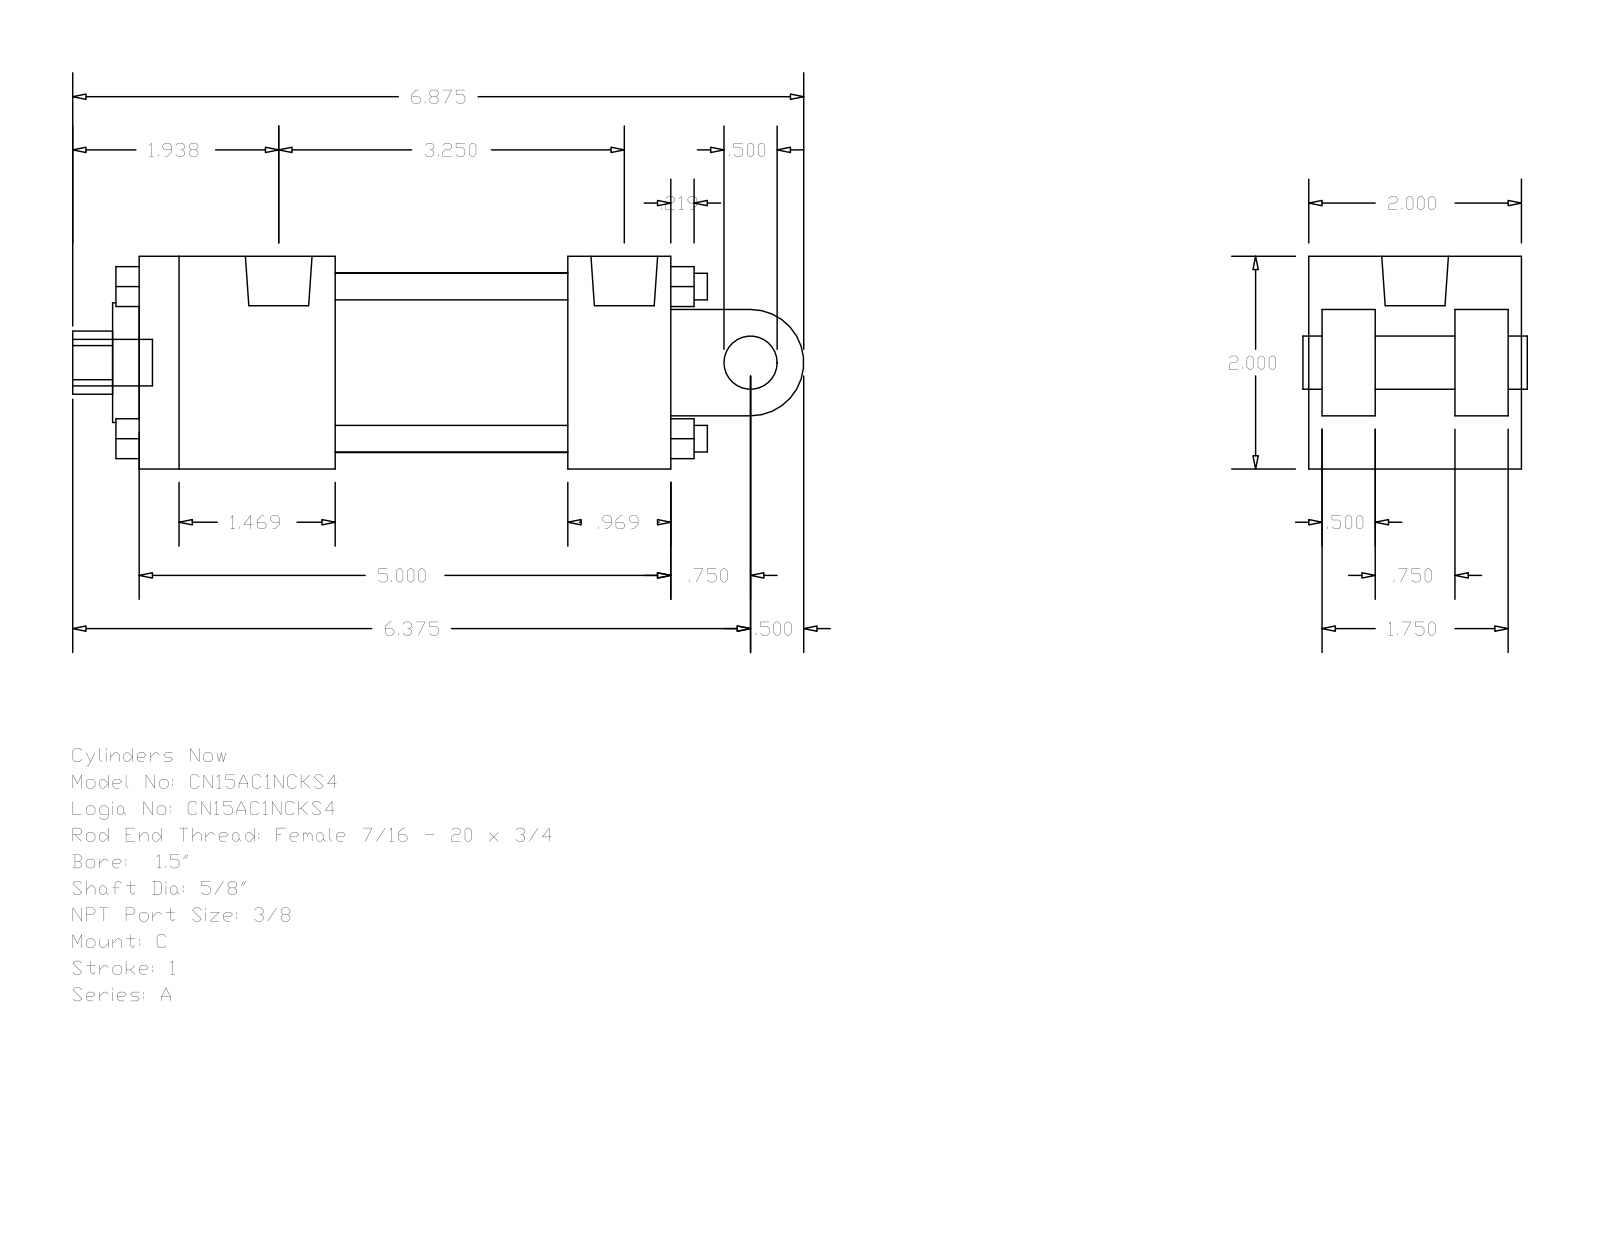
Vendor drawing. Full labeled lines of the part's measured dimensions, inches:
Part name (STEP PRODUCT): A_C__0150_0.625
STEP written by: GSSL Pune (CONFIG_CONTROL_DESIGN)
Units: inches
Bodies: 0 solids, 135 faces (102 planar, 33 cylindrical, 0 other)
Overall size (bounding box): 6.875 × 2 × 2
Round holes (diameter × count): ⌀0.219 ×2, ⌀0.625 ×1, ⌀0.627 ×1, ⌀1.125 ×1, ⌀1.69 ×1
Round bosses / shafts (diameter × count): ⌀0.25 ×4, ⌀0.219 ×2, ⌀0.627 ×1, ⌀0.5 ×1, ⌀0.437 ×1
Partial cylindrical surfaces — rounded edges, fillets, slot ends (radius × count): R0.297 ×1, R0.5 ×1
Main face-to-face distances: 2, 0.5, 5, 0.125, 1.875, 0.625, 1.375, 1.25, 4.031, 0.969
Hole centre spacings: 0.156
